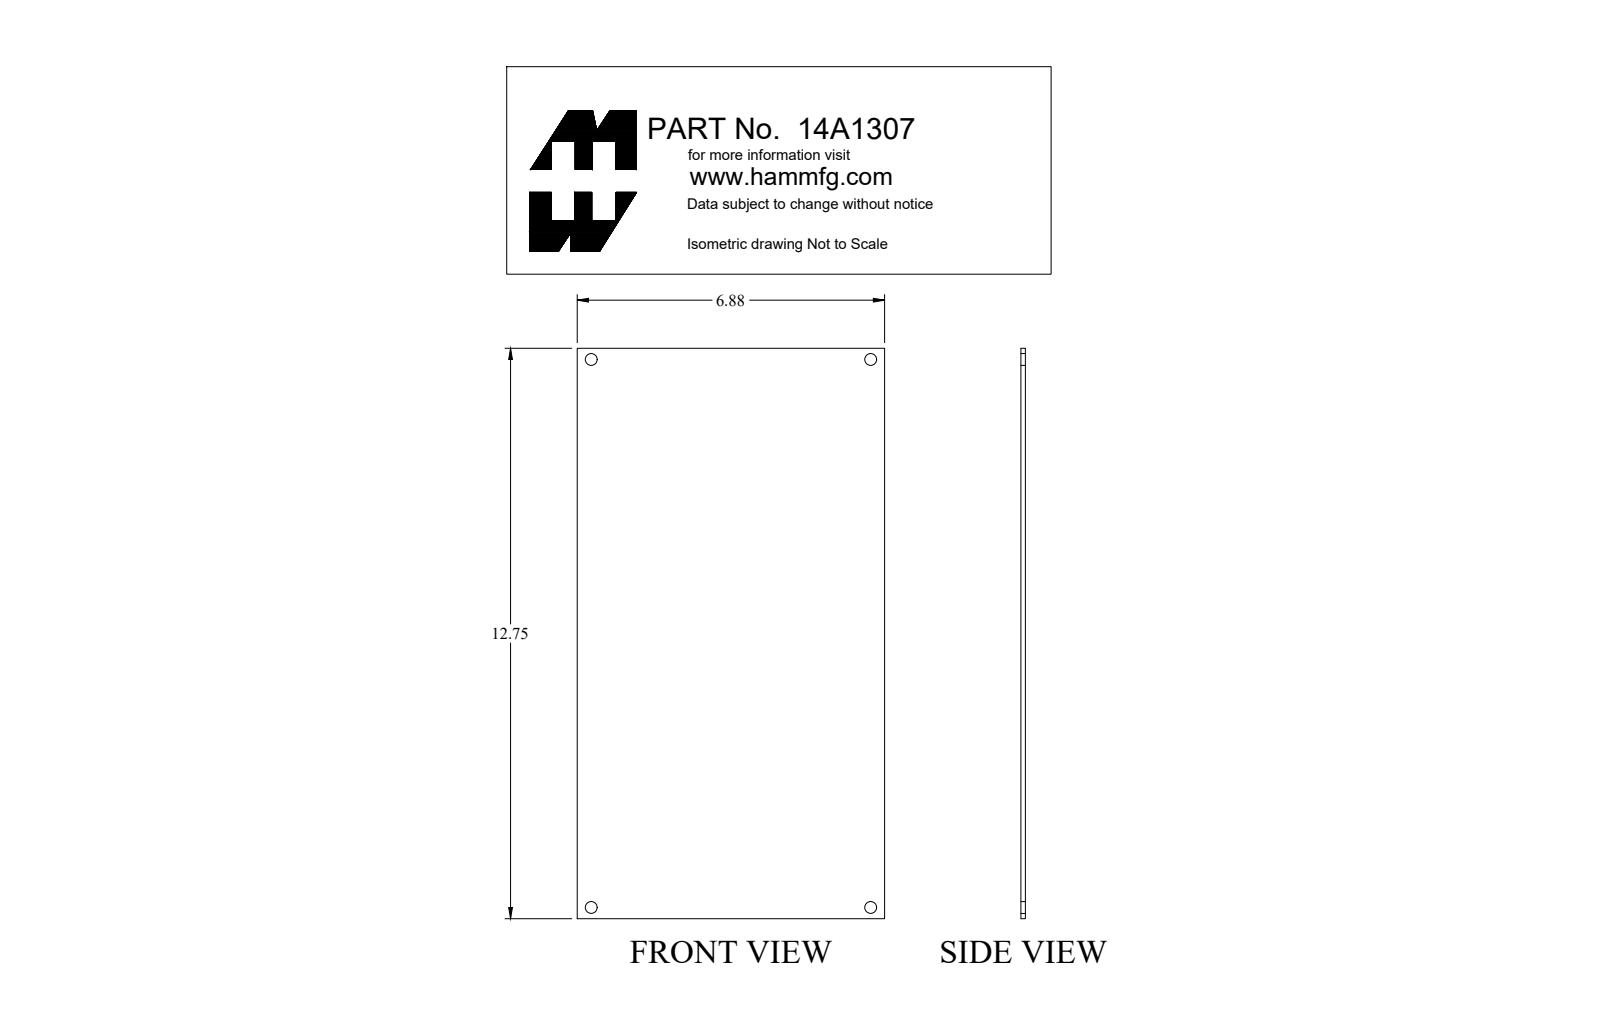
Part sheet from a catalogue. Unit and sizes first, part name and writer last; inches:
Units: inches
Overall size (bounding box): 12.75 × 6.875 × 0.1
Round holes (diameter × count): ⌀0.265 ×4
Main face-to-face distances: 0.1, 6.875, 12.75
Hole centre spacings: 6.251, 12.25, 13.752
Volume: 8.744 in³ · Surface area: 179.1 in²
Bodies: 1 solid, 10 faces (6 planar, 4 cylindrical, 0 other)
Part name (STEP PRODUCT): 14A1307
STEP written by: SolidWorks 2018 (AUTOMOTIVE_DESIGN)
